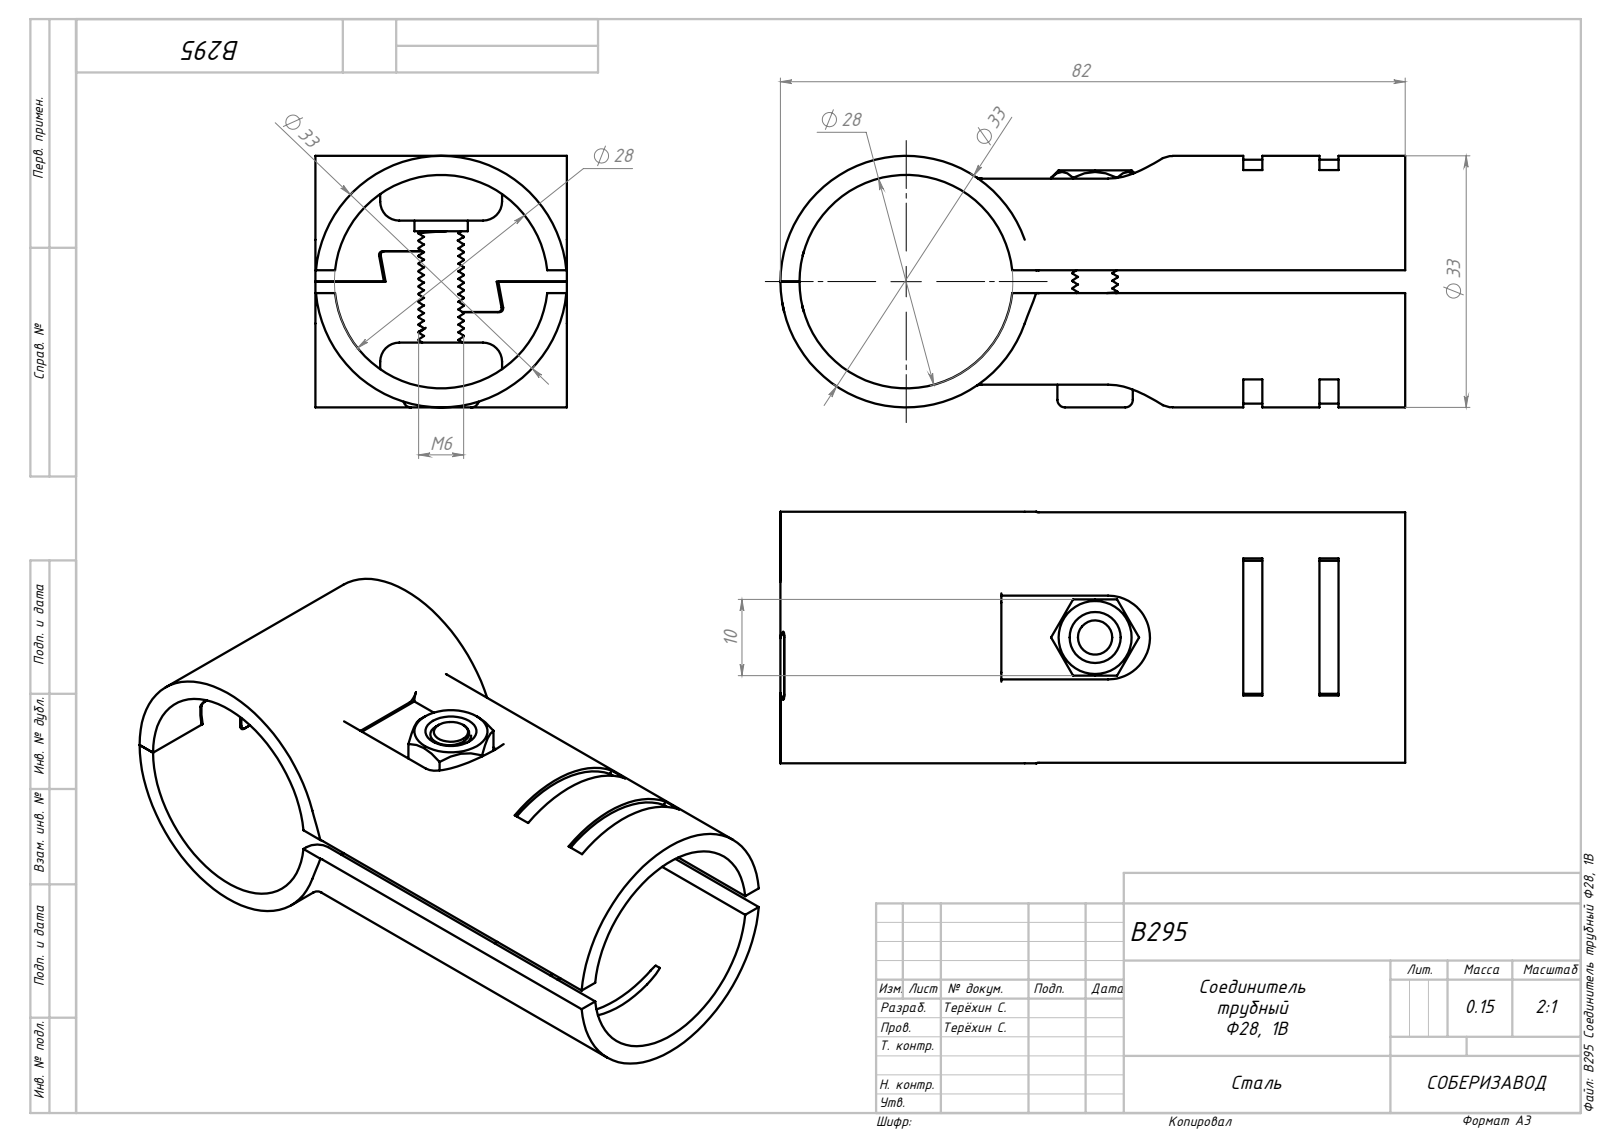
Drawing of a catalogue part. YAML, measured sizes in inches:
part_name: "B295 Соединитель трубный Ф28, 1B"
step_written_by: "SolidWorks 2022 (AUTOMOTIVE_DESIGN)"
units: inches
bodies: {solids: 4, faces: 243, planar: 82, cylindrical: 104, other: 57}
overall_size: [3.228, 1.299, 1.299]
volume: 1.197
surface_area: 28.05
round_holes:
  - {diameter: 1.102, count: 2}
  - {diameter: 0.209, count: 1}
  - {diameter: 0.287, count: 1}
round_bosses_or_shafts:
  - {diameter: 1.299, count: 2}
  - {diameter: 0.39, count: 1}
  - {diameter: 0.276, count: 1}
  - {diameter: 0.232, count: 1}
partial_cylinders:
  - {radius: 0.02, count: 8}
  - {radius: 0.012, count: 6}
  - {radius: 0.098, count: 4}
  - {radius: 0.117, count: 4}
  - {radius: 0.197, count: 2}
  - {radius: 0.636, count: 2}
  - {radius: 0.217, count: 1}
  - {radius: 0.315, count: 1}
face_to_face_distances: [0.472, 0.354, 0.098, 0.256, 0.728, 0.118, 0.374, 1.299, 0.315, 0.827]
